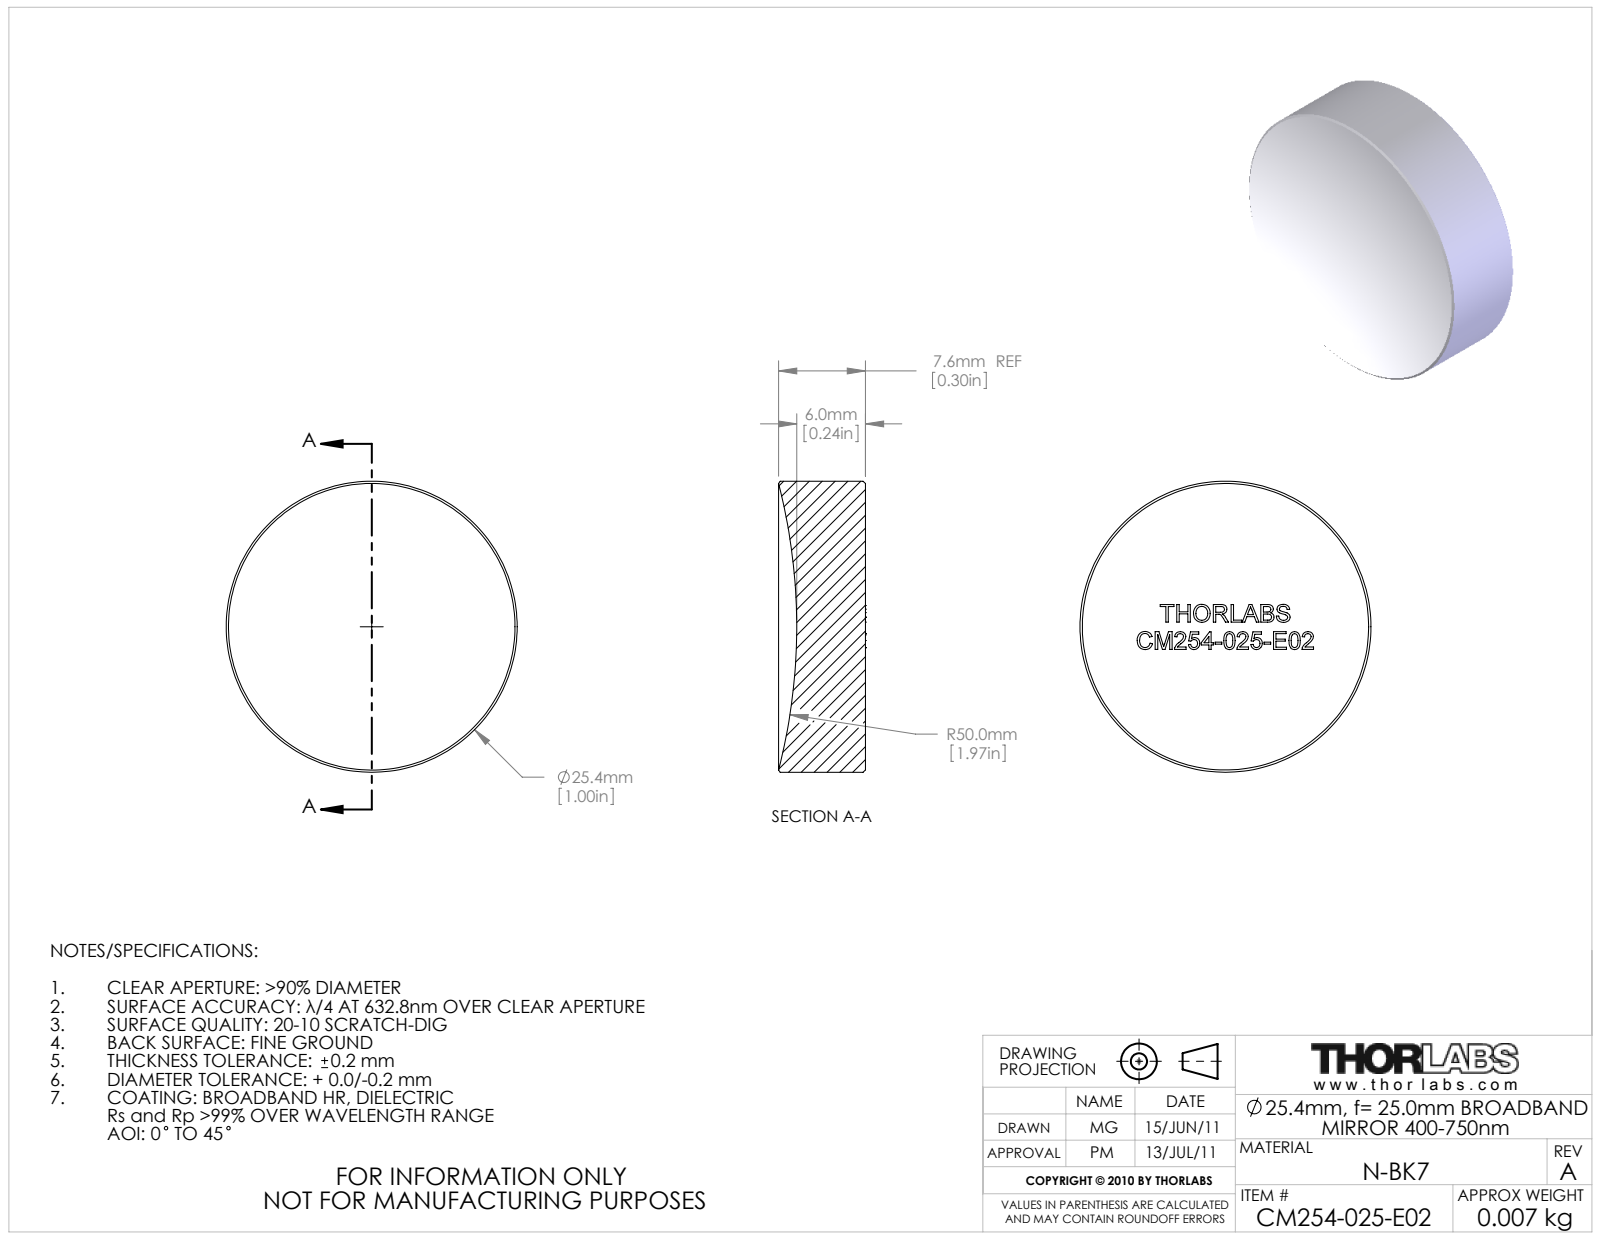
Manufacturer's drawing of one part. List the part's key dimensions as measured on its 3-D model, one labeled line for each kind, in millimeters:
Part name (STEP PRODUCT): 22626-E0W
STEP written by: SolidWorks 2011 (AUTOMOTIVE_DESIGN)
Units: millimetres
Bodies: 0 solids, 44 faces (33 planar, 2 cylindrical, 9 other)
Overall size (bounding box): 25.4 × 25.4 × 7.59
Round bosses / shafts (diameter × count): ⌀25.4 ×1
Main face-to-face distances: 3.91, 3.02, 0.89
